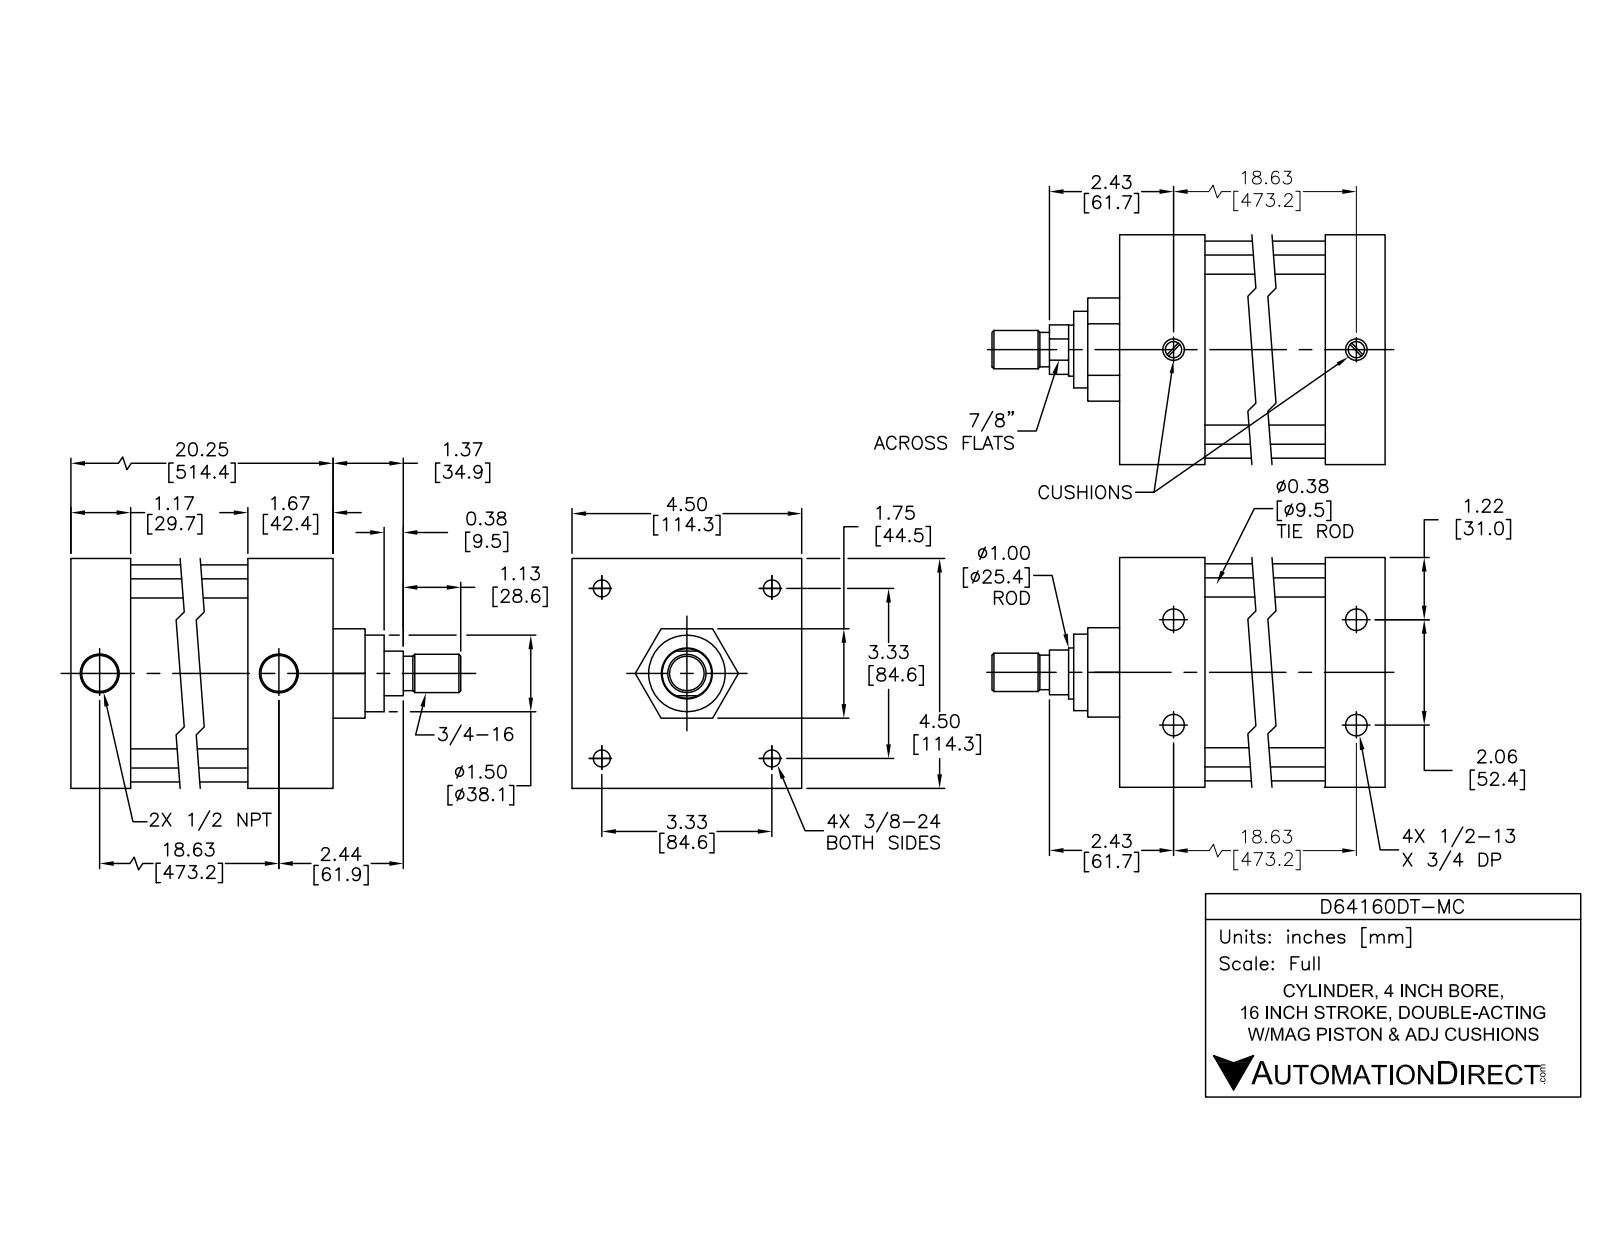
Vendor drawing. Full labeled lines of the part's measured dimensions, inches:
Part name (STEP PRODUCT): D64160DT-M BODY; D64160DT-M PISTON; D64160DT-MC
STEP written by: SolidWorks 2015 (AUTOMOTIVE_DESIGN)
Units: inches
Bodies: 12 solids, 303 faces (99 planar, 114 cylindrical, 90 other)
Overall size (bounding box): 22.745 × 4.5 × 4.5
Volume: 121.6 in³ · Surface area: 823.5 in²
Round holes (diameter × count): ⌀0.33 ×4, ⌀0.406 ×4, ⌀0.417 ×4, ⌀0.625 ×4, ⌀0.5 ×2, ⌀0.766 ×2, ⌀1 ×1, ⌀1.003 ×1, ⌀4 ×1
Round bosses / shafts (diameter × count): ⌀0.609 ×4, ⌀0.375 ×4, ⌀0.34 ×4, ⌀4.25 ×1, ⌀3.997 ×1, ⌀1.75 ×1, ⌀0.997 ×1, ⌀0.97 ×1
Partial cylindrical surfaces — rounded edges, fillets, slot ends (radius × count): R0.45 ×4
Main face-to-face distances: 4.5, 0.08, 17.326, 20.246, 1.75, 18.997, 1.249, 17.751, 1.246, 2.495
Hole centre spacings: 2.349, 3.322, 18.65, 18.622, 1.031, 1.031, 2.062, 4.698
